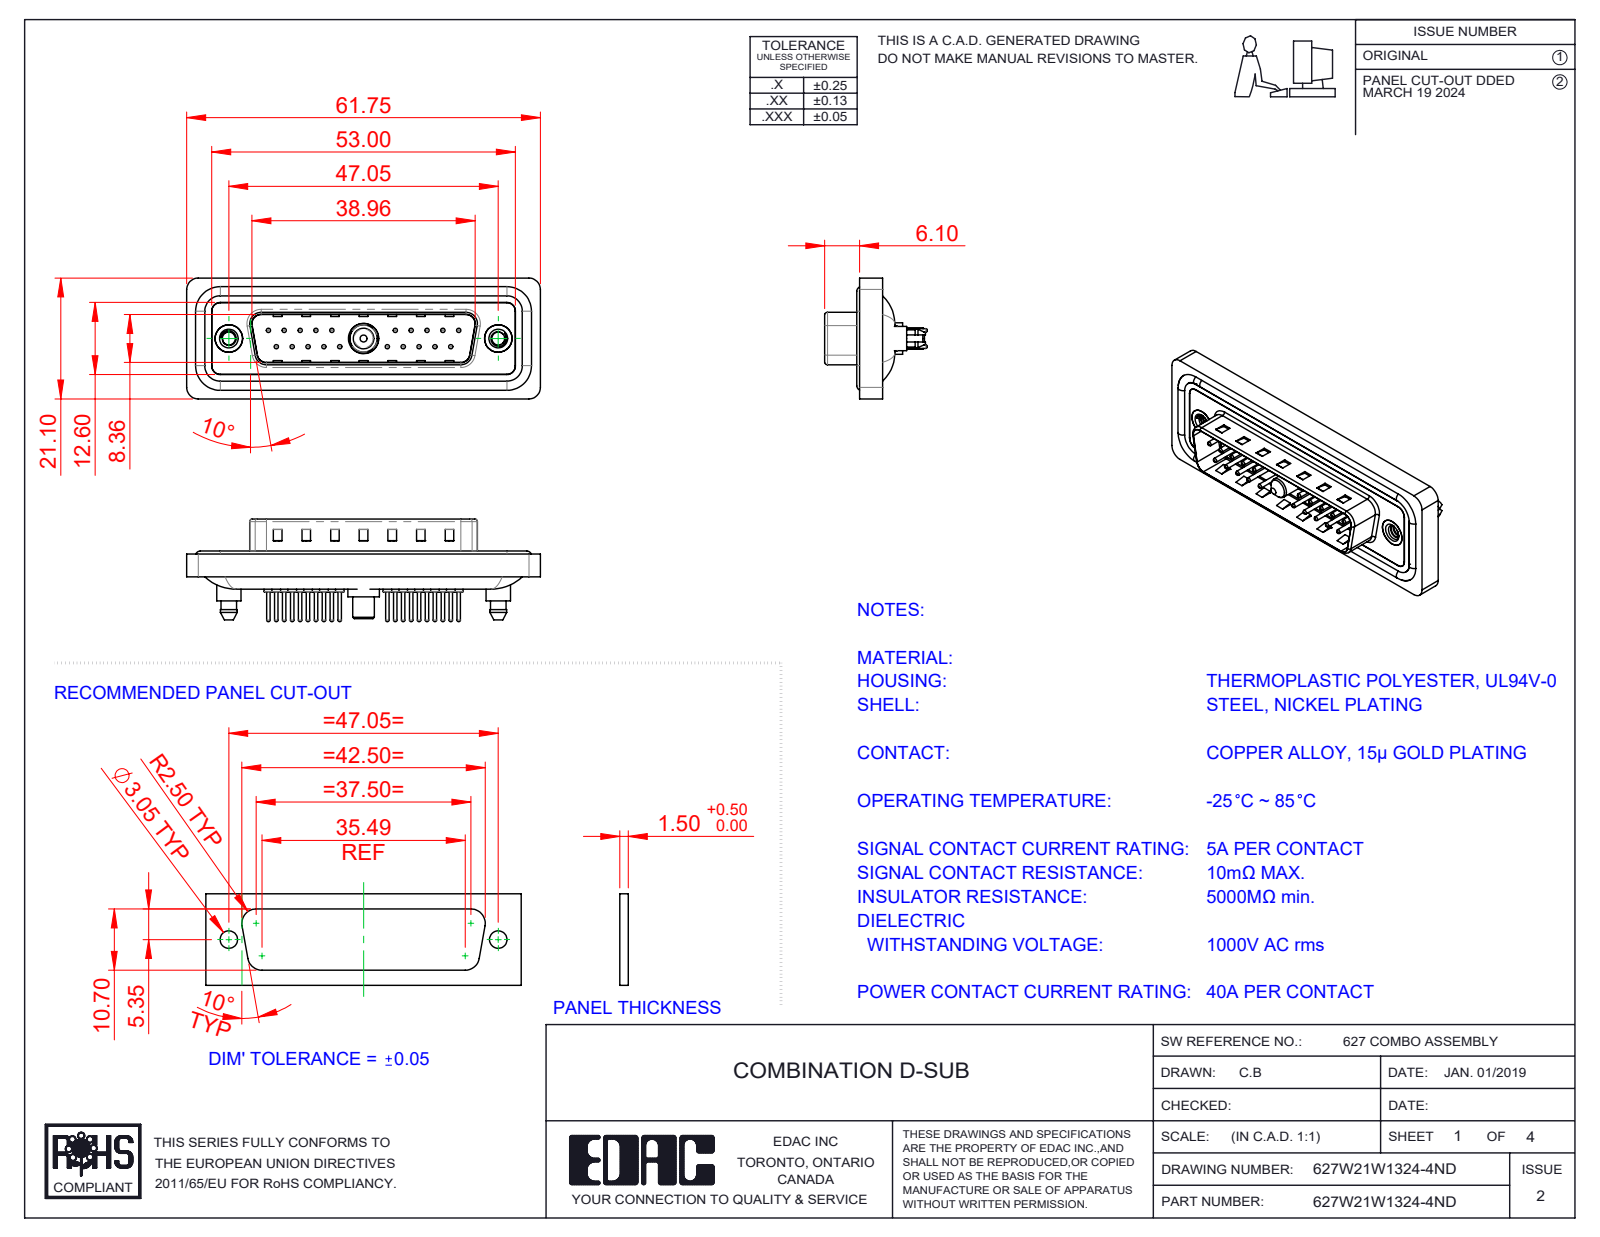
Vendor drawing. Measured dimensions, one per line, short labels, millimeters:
name: 627Combo Contact Row 1_24; Power Pin_40A S; 627W21W1324-4ND; 627Combo Housing_21W1 (+6 more)
written by: SolidWorks 2023 (CONFIG_CONTROL_DESIGN)
unit: mm
bodies: 29 solids, 1320 faces (375 planar, 527 cylindrical, 418 other)
size: 61.75 × 21.1 × 17.9
volume: 7 351 mm³; area: 12 300 mm²
holes: 20× ⌀0.75, 20× ⌀1.6, 20× ⌀2, 2× ⌀2.26, 2× ⌀4, 2× ⌀4.8, 2× ⌀5, 1× ⌀4.85, 1× ⌀5.3
bosses: 20× ⌀1.5, 20× ⌀0.6, 4× ⌀1.6, 2× ⌀5.4, 2× ⌀4.9, 2× ⌀4.25, 1× ⌀5.5, 1× ⌀5.2
rounds: 24× R1.5, 18× R2, 10× R1.6, 8× R0.5, 4× R0.25, 4× R0.6, 4× R0.65, 4× R0.9
face distances: 0.4, 1.5, 1.1, 1.6, 3.1, 0.5, 2.9, 4.1, 0.82, 9.58
hole spacings: 3.16, 2.77, 5.54, 8.31, 5.04, 19.39, 20.97, 22.16
